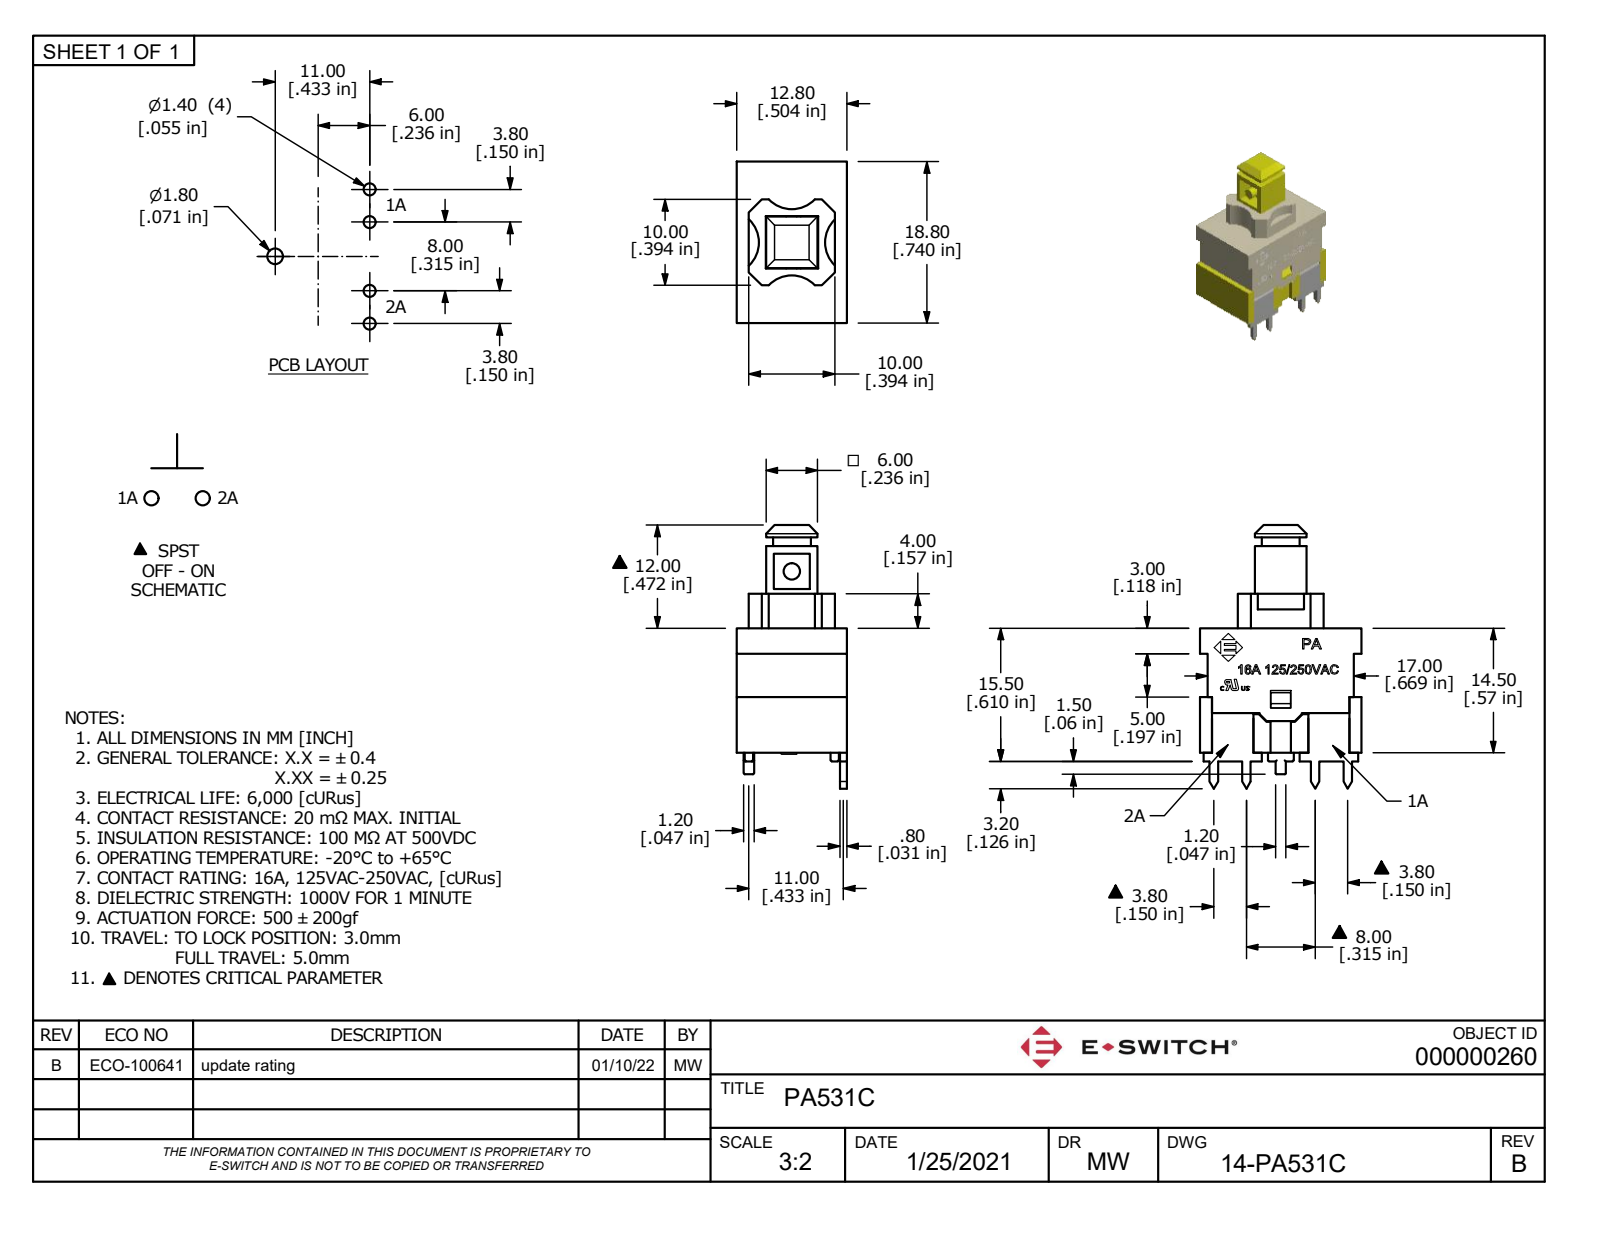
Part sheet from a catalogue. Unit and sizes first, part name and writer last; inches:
Units: inches
Overall size (bounding box): 1.209 × 0.74 × 0.504
Round holes (diameter × count): ⌀0.118 ×1
Round bosses / shafts (diameter × count): ⌀0.037 ×4, ⌀0.098 ×1, ⌀0.075 ×1
Partial cylindrical surfaces — rounded edges, fillets, slot ends (radius × count): R0.01 ×17, R0.005 ×16, R0.006 ×8, R0.146 ×4, R0.039 ×2, R0.02 ×1, R0.024 ×1, R0.07 ×1
Main face-to-face distances: 0.031, 0.472, 0.035, 0.661, 0.079, 0.339, 0.173, 0.043, 0.504, 0.203
Volume: 0.129 in³ · Surface area: 6.55 in²
Bodies: 1 solid, 770 faces (576 planar, 64 cylindrical, 130 other)
Part name (STEP PRODUCT): PA531C
STEP written by: Autodesk Inventor 2022 (AUTOMOTIVE_DESIGN)
